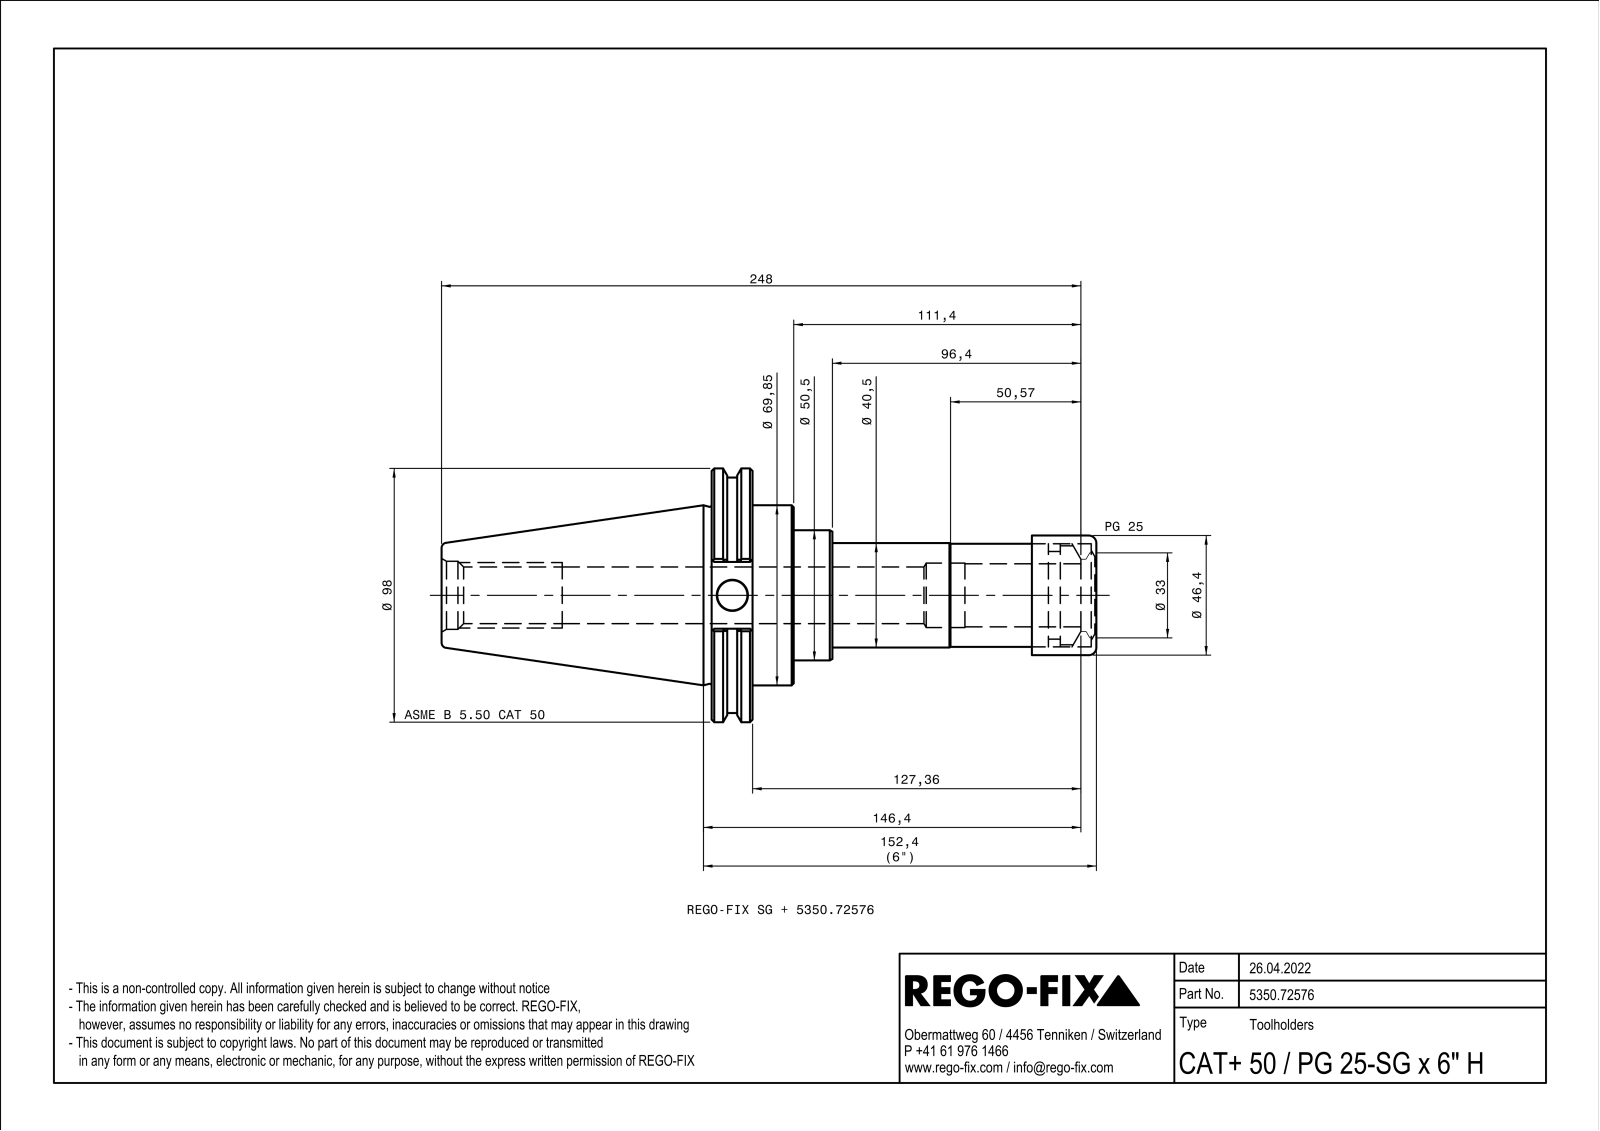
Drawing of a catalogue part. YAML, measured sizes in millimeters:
part_name: "NOCUT"
step_written_by: "SIEMENS PLM Software Solid Edge ST10 (AUTOMOTIVE_DESIGN)"
units: millimeters
bodies: {solids: 1, faces: 130, planar: 56, cylindrical: 27, other: 47}
overall_size: [254, 98.43, 94.43]
volume: 488140
surface_area: 78464
round_holes:
  - {diameter: 12, count: 1}
  - {diameter: 21.96, count: 1}
  - {diameter: 25, count: 1}
  - {diameter: 26.4, count: 1}
  - {diameter: 30, count: 1}
  - {diameter: 40.05, count: 1}
  - {diameter: 42, count: 1}
round_bosses_or_shafts:
  - {diameter: 98.43, count: 1}
  - {diameter: 91.3, count: 1}
  - {diameter: 69.85, count: 1}
  - {diameter: 69.25, count: 1}
  - {diameter: 50.5, count: 1}
  - {diameter: 46.4, count: 1}
  - {diameter: 46, count: 1}
  - {diameter: 40.5, count: 1}
partial_cylinders:
  - {radius: 0.5, count: 4}
face_to_face_distances: [17.55, 16, 33.55, 133.35, 117.35, 150.9, 254, 136.65, 120.65, 103.1]
